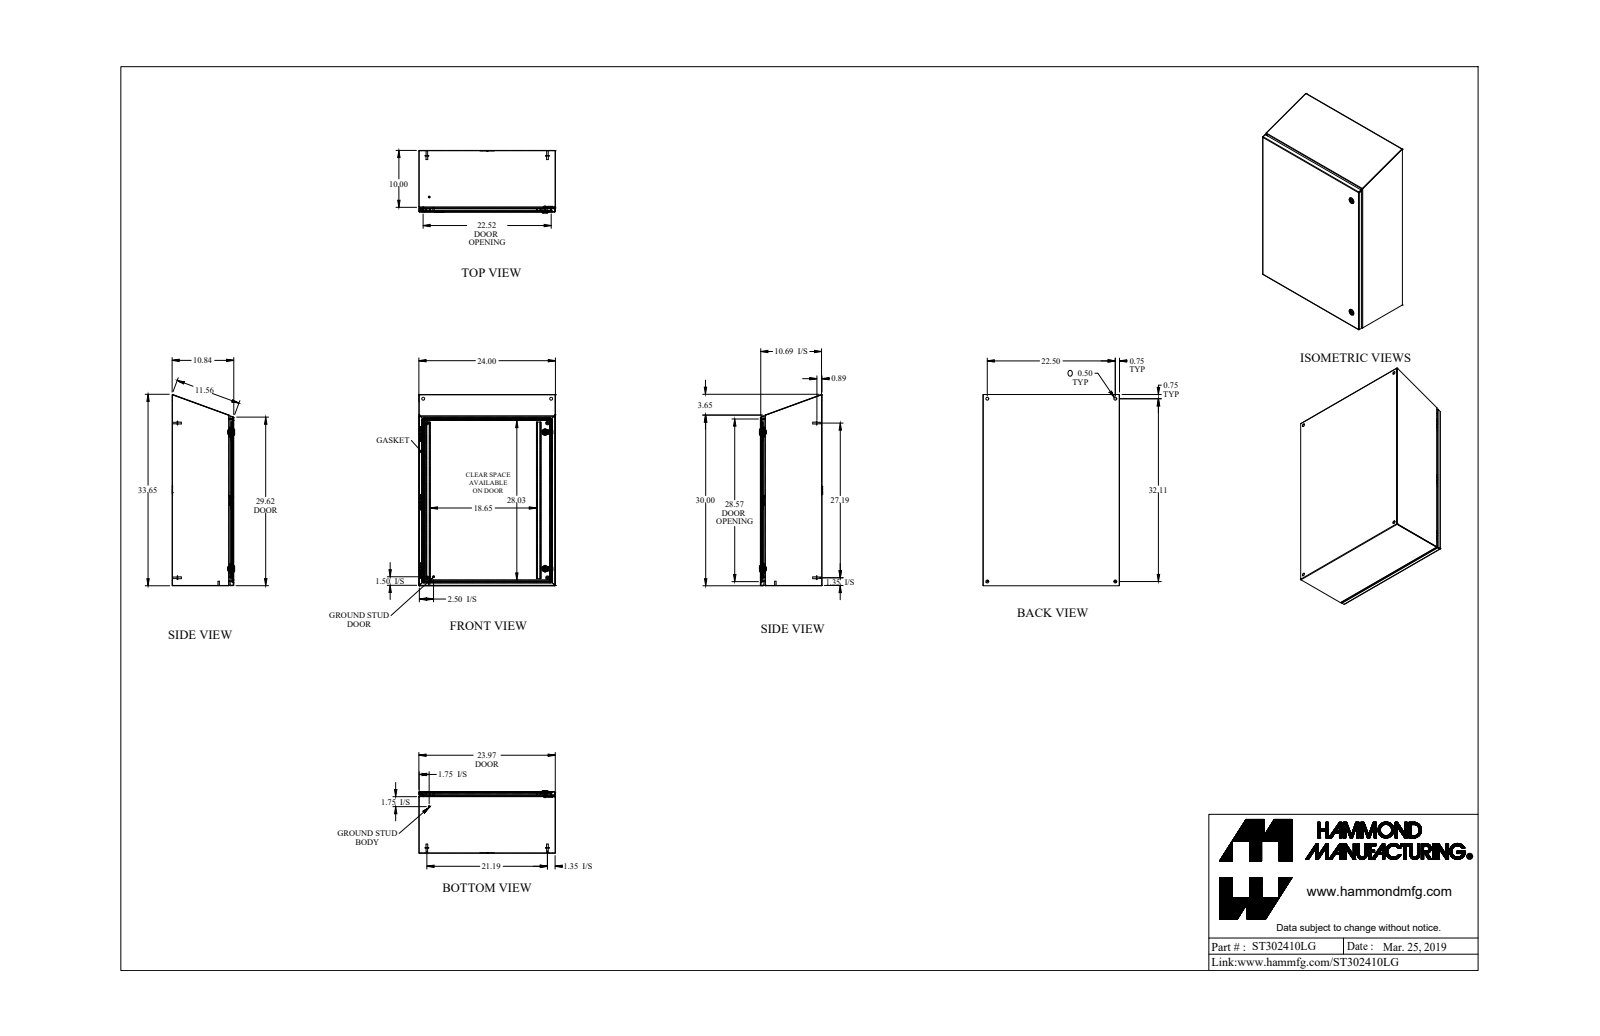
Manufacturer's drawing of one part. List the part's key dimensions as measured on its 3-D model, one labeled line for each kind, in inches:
Part name (STEP PRODUCT): ST302410LG
STEP written by: SolidWorks 2018 (AUTOMOTIVE_DESIGN)
Units: inches
Bodies: 33 solids, 868 faces (430 planar, 286 cylindrical, 152 other)
Overall size (bounding box): 33.614 × 24 × 10.997
Volume: 189.5 in³ · Surface area: 6 186 in²
Round holes (diameter × count): ⌀0.5 ×4, ⌀0.232 ×2, ⌀0.625 ×2, ⌀0.785 ×2, ⌀0.172 ×1, ⌀0.24 ×1, ⌀0.242 ×1
Round bosses / shafts (diameter × count): ⌀0.625 ×4, ⌀0.313 ×4, ⌀0.27 ×4, ⌀1.1 ×2, ⌀0.525 ×2, ⌀0.281 ×2, ⌀0.25 ×2, ⌀0.455 ×1
Partial cylindrical surfaces — rounded edges, fillets, slot ends (radius × count): R0.029 ×15, R0.086 ×15, R0.188 ×13, R0.043 ×12, R0.081 ×12, R0.006 ×6, R0.062 ×6, R0.036 ×4
Main face-to-face distances: 0.057, 10.765, 10.708, 0.072, 10.837, 10.78, 23.943, 23.886, 24, 0.057
Hole centre spacings: 22.5, 32.114, 39.211, 2.494, 5.96, 21.544, 22.213, 24
